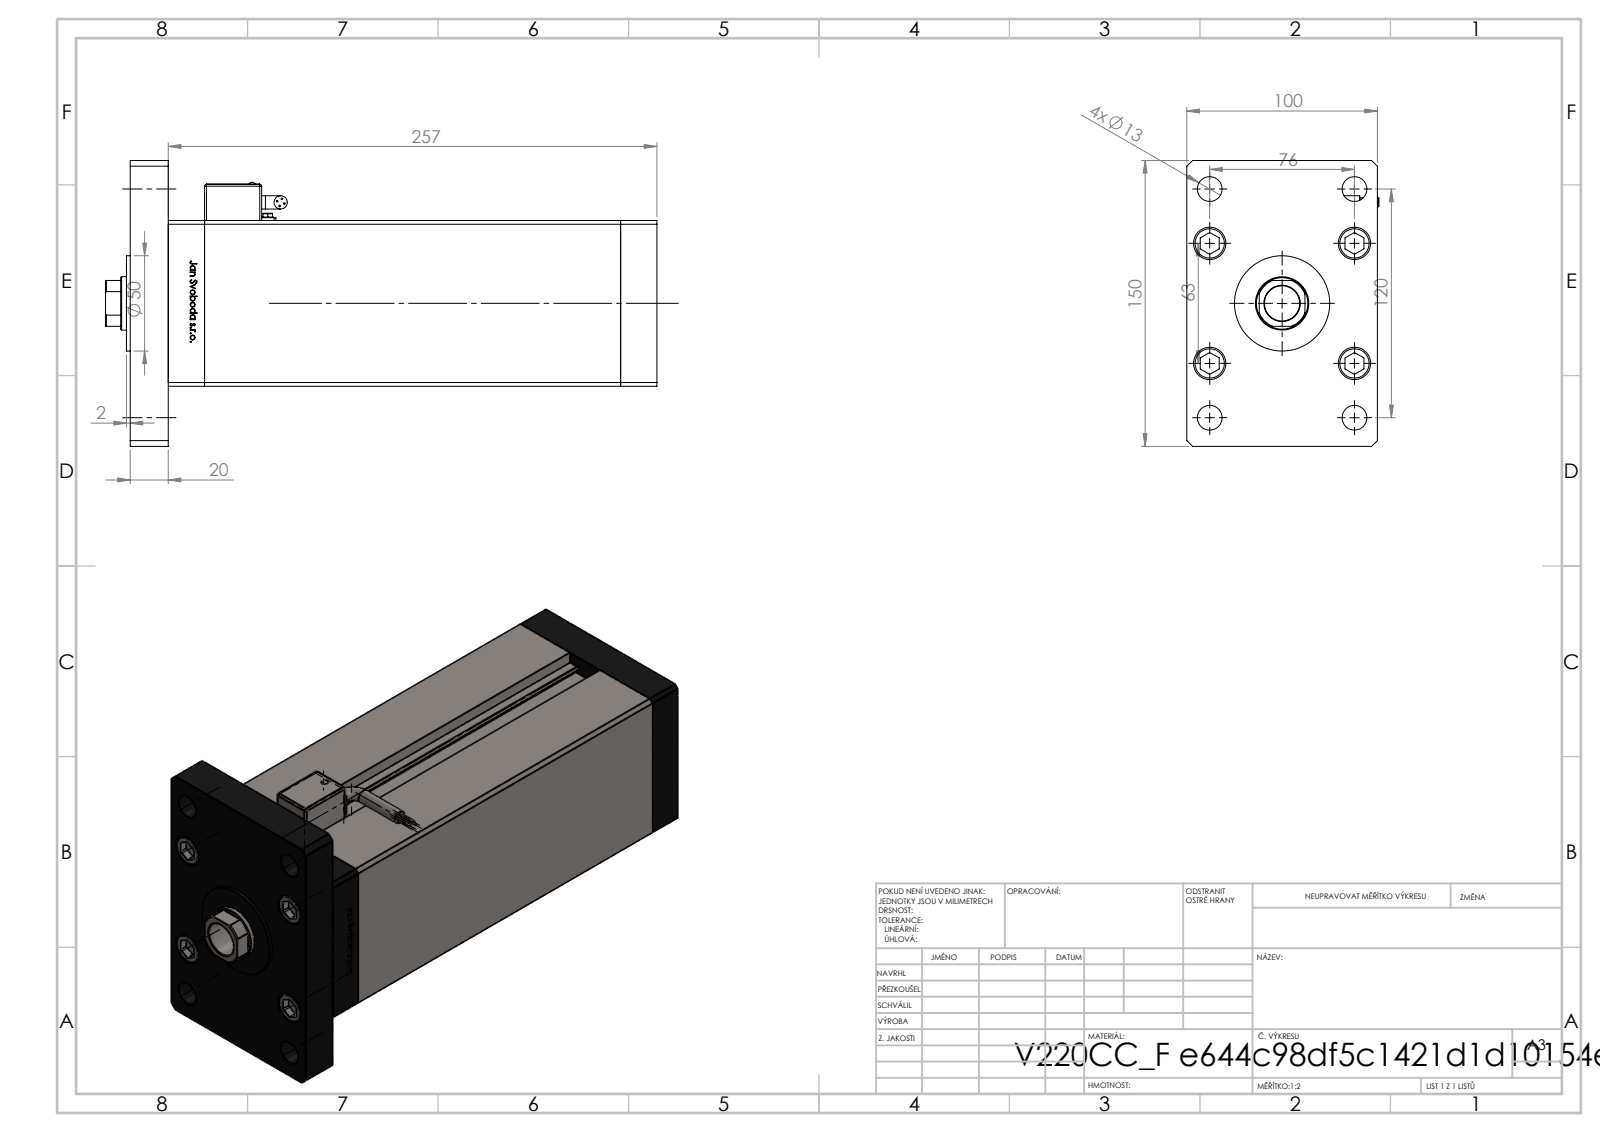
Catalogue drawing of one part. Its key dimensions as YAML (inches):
part_name: "V220C_F_MIDDLE; V220C BACK_F; Magnetic_Switch_MSU4; ALLEN BOLT (+3 more)"
step_written_by: "SolidWorks 2019 (CONFIG_CONTROL_DESIGN)"
units: inches
bodies: {solids: 20, faces: 1413, planar: 556, cylindrical: 233, other: 624}
overall_size: [11.398, 5.906, 3.969]
volume: 135.7
surface_area: 480.1
round_holes:
  - {diameter: 0.531, count: 7}
  - {diameter: 0.709, count: 7}
  - {diameter: 0.472, count: 4}
  - {diameter: 0.512, count: 4}
  - {diameter: 0.669, count: 4}
  - {diameter: 0.079, count: 2}
  - {diameter: 0.518, count: 2}
  - {diameter: 0.142, count: 1}
  - {diameter: 0.197, count: 1}
  - {diameter: 0.276, count: 1}
  - {diameter: 0.728, count: 1}
  - {diameter: 1.102, count: 1}
round_bosses_or_shafts:
  - {diameter: 0.315, count: 9}
  - {diameter: 0.669, count: 5}
  - {diameter: 0.033, count: 4}
  - {diameter: 0.276, count: 2}
  - {diameter: 1.969, count: 1}
  - {diameter: 0.236, count: 1}
  - {diameter: 0.138, count: 1}
  - {diameter: 0.098, count: 1}
partial_cylinders:
  - {radius: 0.039, count: 14}
  - {radius: 0.037, count: 2}
  - {radius: 0.157, count: 2}
  - {radius: 0.531, count: 1}
face_to_face_distances: [3.937, 0.748, 3.425, 9.35, 0.787, 8.602, 1.535, 10.138, 10.098, 10.886]
hole_center_spacings: [1.339, 0.732, 1.122, 1.462, 1.561, 1.943, 2.281, 2.796]
